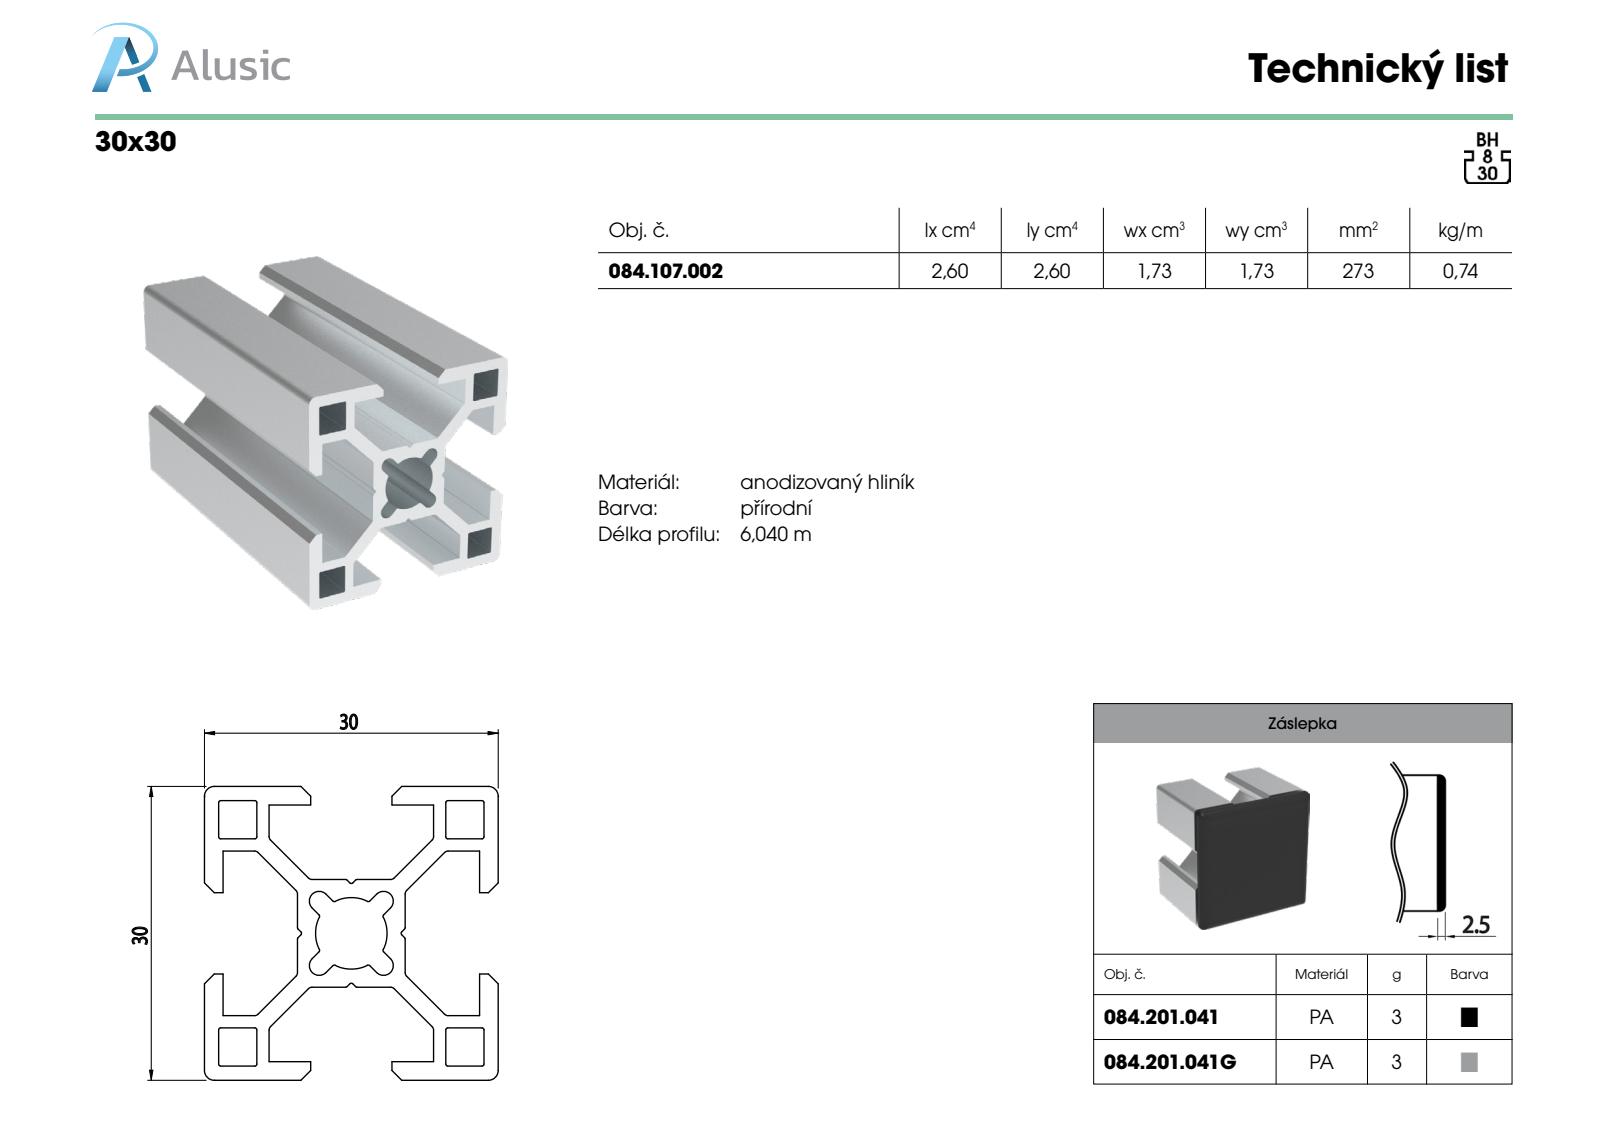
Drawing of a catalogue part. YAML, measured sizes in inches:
part_name: "084.107.002"
step_written_by: "SolidWorks 2018 (AUTOMOTIVE_DESIGN)"
units: inches
bodies: {solids: 1, faces: 160, planar: 90, cylindrical: 70, other: 0}
overall_size: [3.937, 1.181, 1.181]
volume: 1.665
surface_area: 52.95
partial_cylinders:
  - {radius: 0.008, count: 36}
  - {radius: 0.02, count: 16}
  - {radius: 0.039, count: 8}
  - {radius: 0.144, count: 1}
face_to_face_distances: [0.075, 1.181, 1.106, 0.057, 1.124, 0.018, 1.049, 0.211, 0.97, 0.136]
